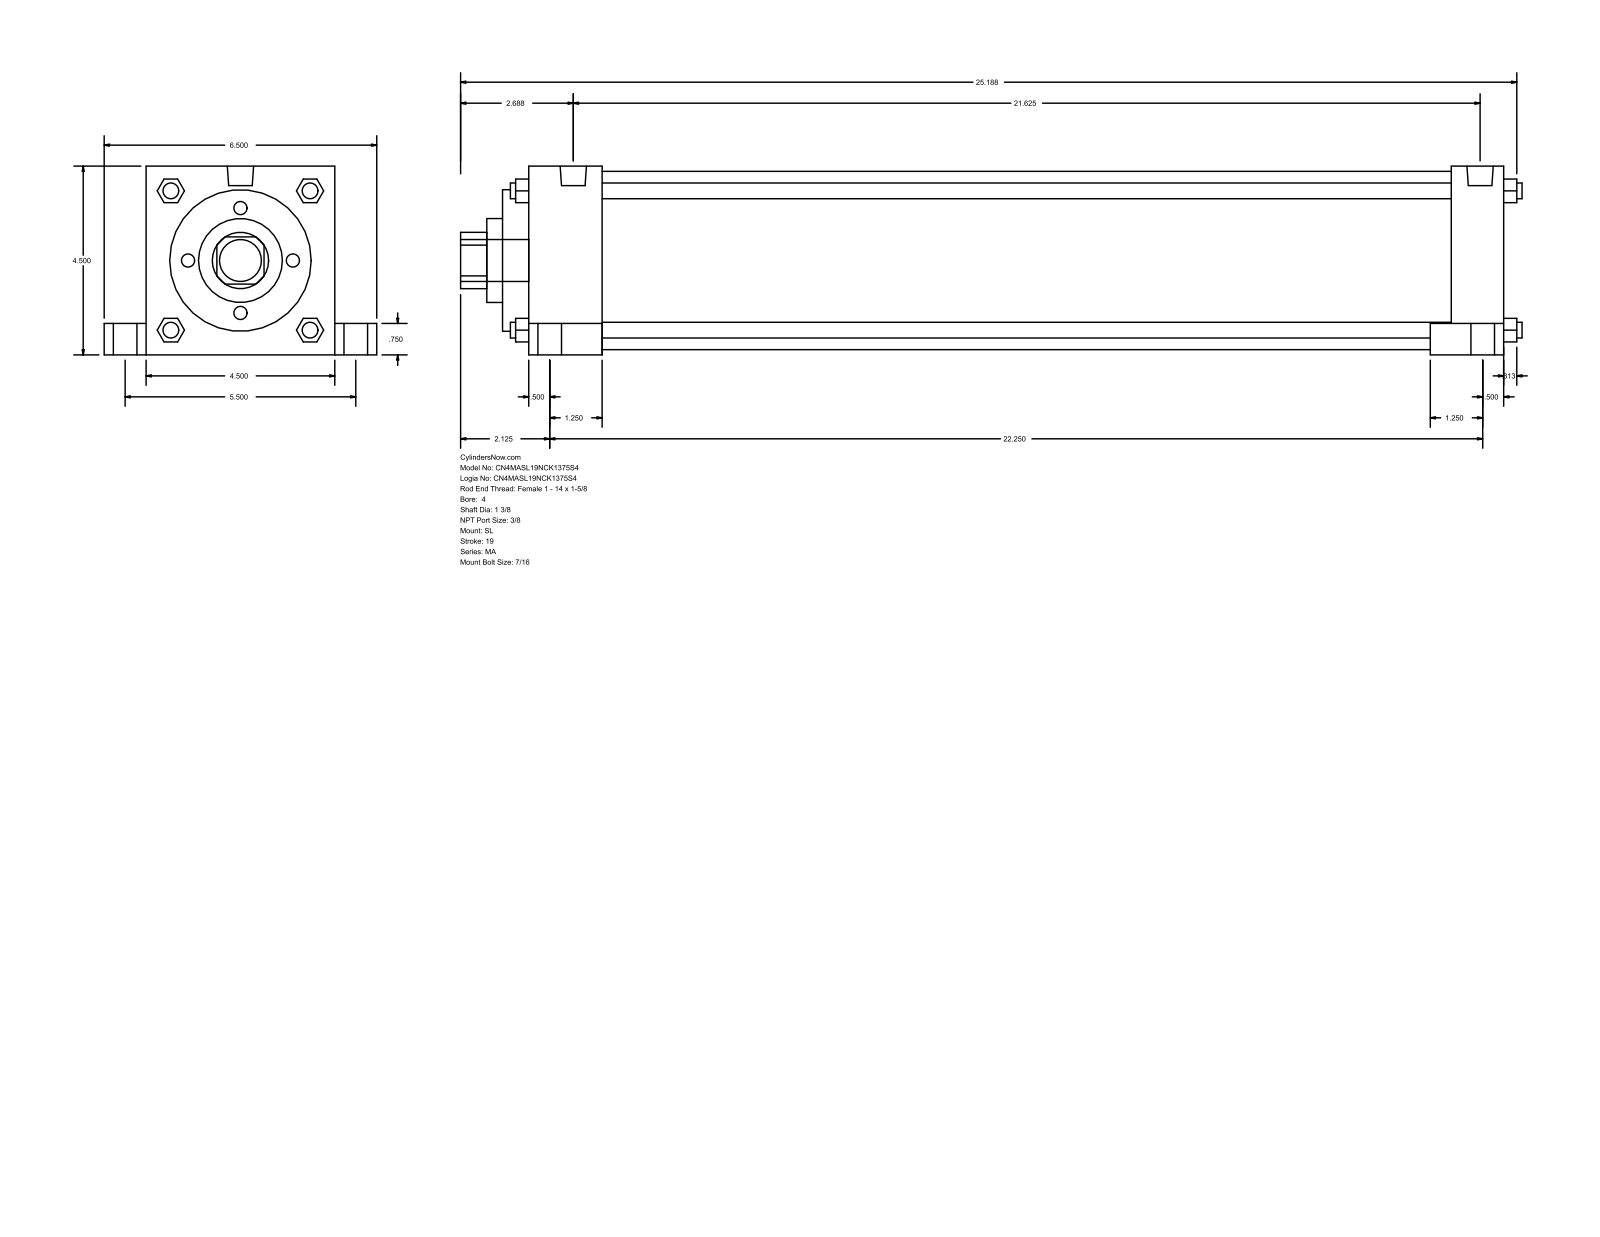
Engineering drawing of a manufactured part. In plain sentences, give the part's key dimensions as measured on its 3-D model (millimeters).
The part is named "MA_SL__0400_1.375". Its 3-D file was written by "GSSL Pune (CONFIG_CONTROL_DESIGN)". It is 0 solids with 150 faces: 113 planar, 37 cylindrical and 0 other. Overall it measures 642.94 by 165.1 by 114.3 millimeters. Round holes: 1 of diameter 34.92, 1 of diameter 50.8, 1 of diameter 85.72, 1 of diameter 107.95. Round bosses or shafts: 4 of diameter 20.64, 4 of diameter 14.29, 4 of diameter 11.11, 4 of diameter 9.53, 2 of diameter 15.93, 1 of diameter 25.4. Partial cylindrical surfaces (rounded edges, fillets, slot ends): 1 of radius 17.06. The main face-to-face distances are 114.3, 590.56, 15.87, 606.43, 60.32, 44.45, 546.11, 574.68, 558.81, 514.36.
